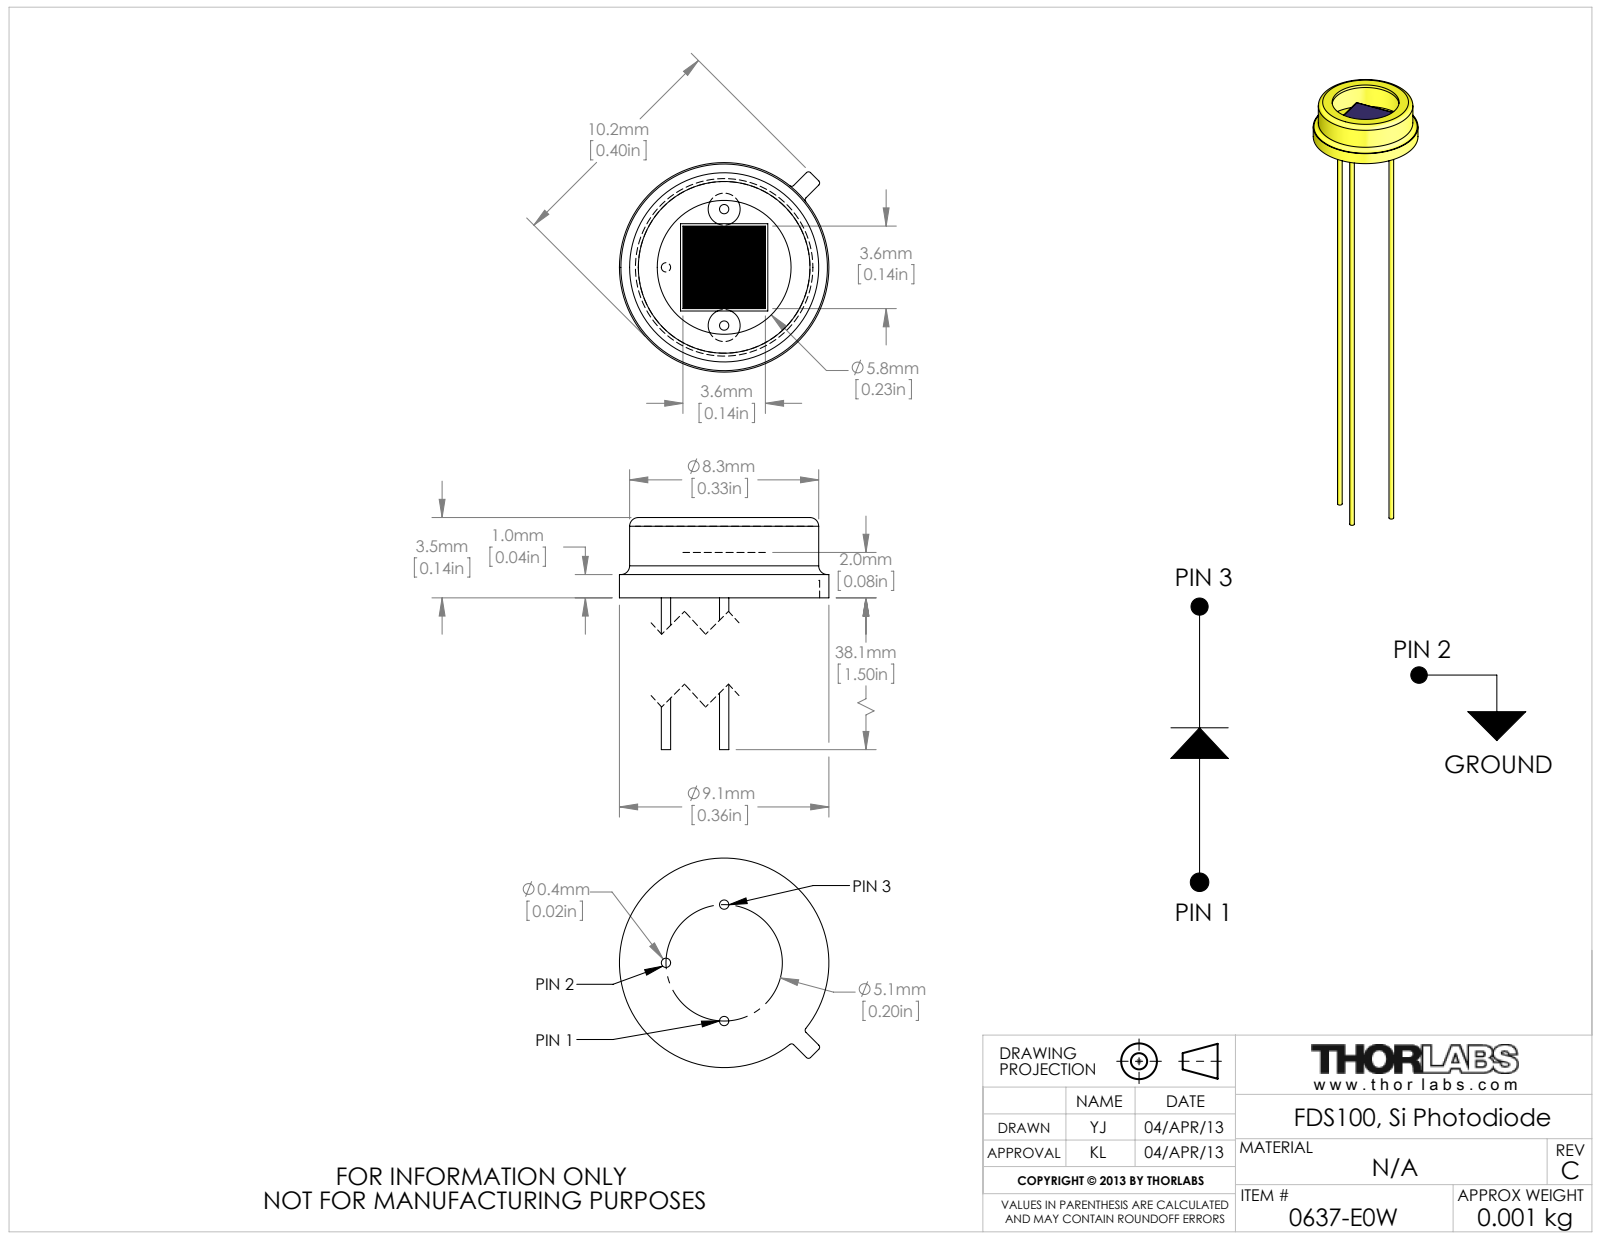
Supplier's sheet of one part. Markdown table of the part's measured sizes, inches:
| quantity | value |
| --- | --- |
| part name | 0637-E0W |
| STEP written by | SolidWorks 2012 (AUTOMOTIVE_DESIGN) |
| units | inches |
| bodies | 1 solid, 61 faces (28 planar, 27 cylindrical, 6 other) |
| overall size | 1.638 × 0.36 × 0.36 |
| volume | 0.007 in³ |
| surface area | 0.762 in² |
| round holes (diameter × count) | 0.055 × 2, 0.23 × 1, 0.305 × 1 |
| round bosses / shafts (diameter × count) | 0.016 × 3, 0.36 × 1, 0.325 × 1 |
| partial cylindrical surfaces (radius × count) | 0.005 × 4 |
| main face-to-face distances | 0.03, 0.098, 0.128, 0.138, 0.108, 0.078, 0.048, 0.05, 0.06, 0.02 |
| hole center spacings | 0.1, 0.2 |
